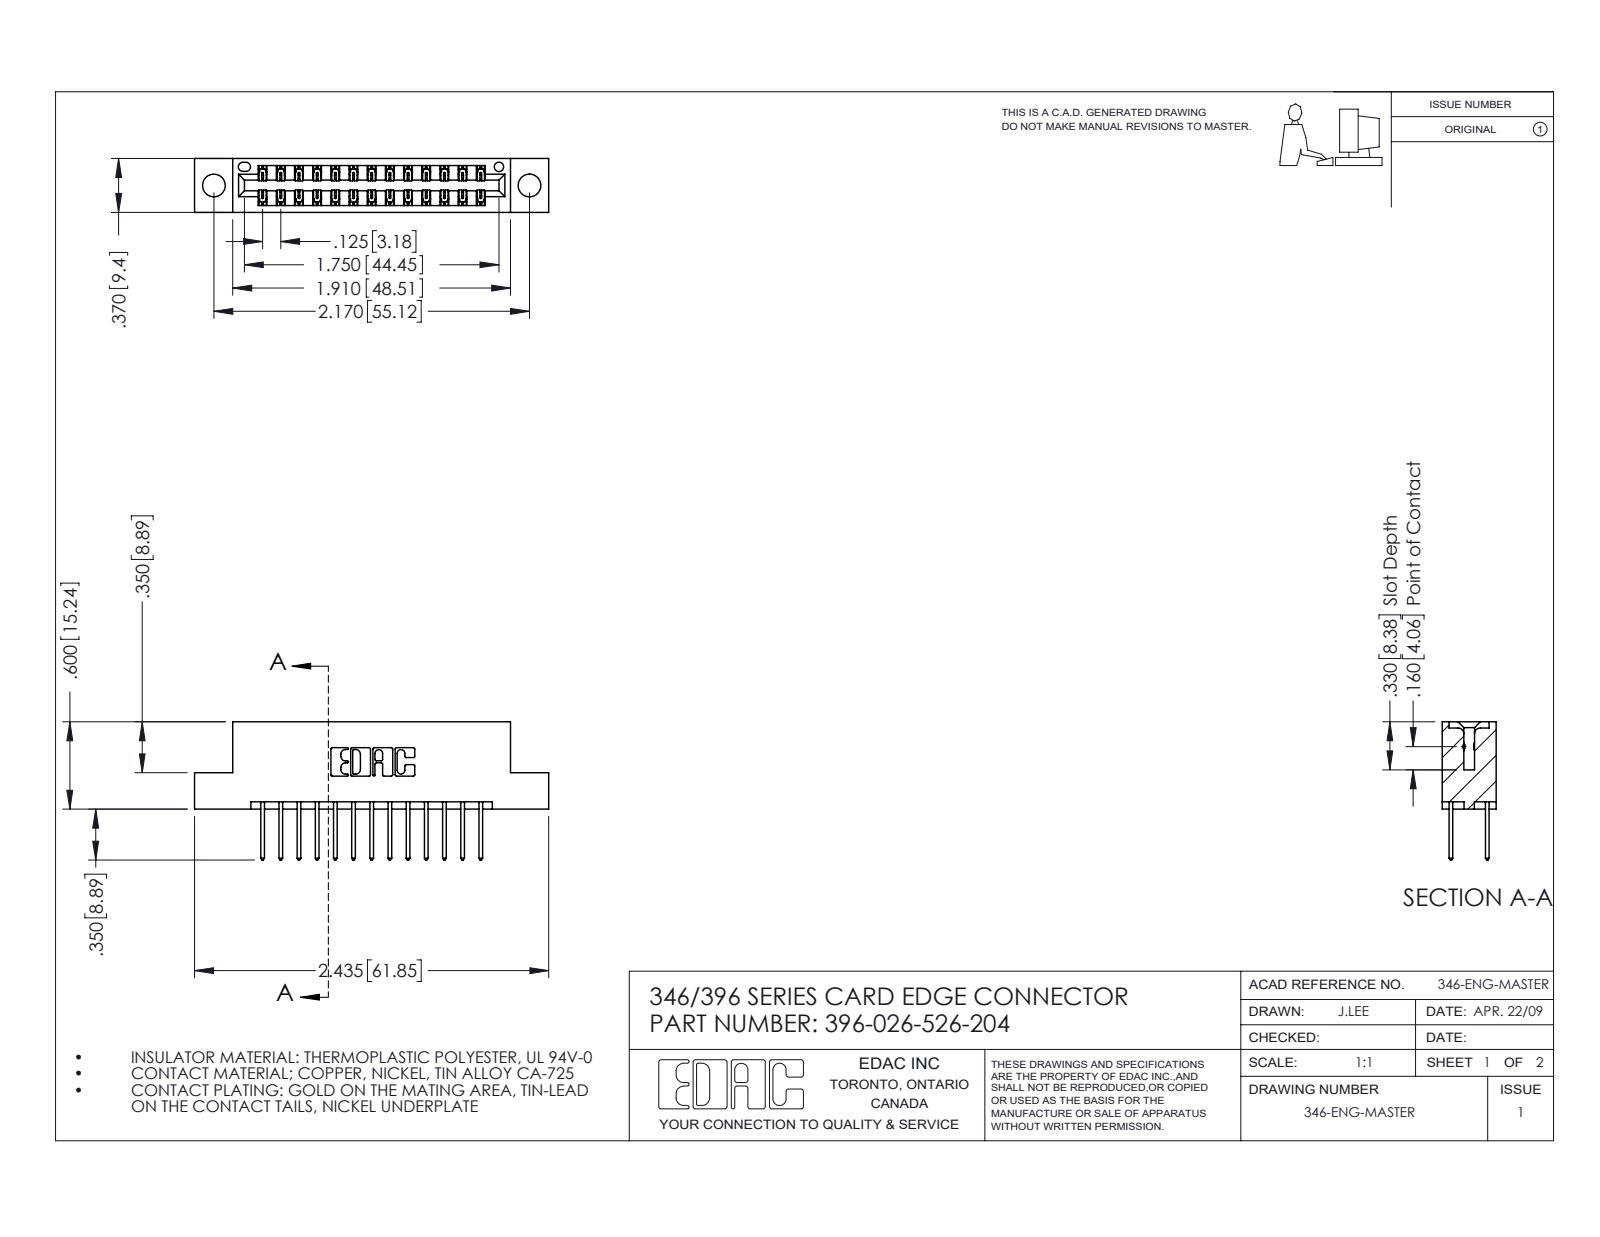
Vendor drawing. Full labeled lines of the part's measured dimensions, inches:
Part name (STEP PRODUCT): 346 Part_Flush Mounting Lugs - 0.156 Dia-TH; 396-026-526-204; 345-292-001_345-293-126
STEP written by: SolidWorks 2016 (CONFIG_CONTROL_DESIGN)
Units: inches
Bodies: 27 solids, 1474 faces (986 planar, 488 cylindrical, 0 other)
Overall size (bounding box): 2.435 × 0.95 × 0.37
Volume: 0.352 in³ · Surface area: 11.57 in²
Round holes (diameter × count): ⌀0.156 ×2, ⌀0.064 ×1
Partial cylindrical surfaces — rounded edges, fillets, slot ends (radius × count): R0.006 ×39, R0.01 ×26, R0.01 ×22, R0.007 ×6, R0.031 ×6, R0.026 ×3, R0.014 ×2, R0.022 ×2
Main face-to-face distances: 0.25, 0.048, 0.322, 0.37, 0.072, 0.298, 0.025, 0.275, 0.148, 0.222
Hole centre spacings: 0.246, 1.964, 2.17
